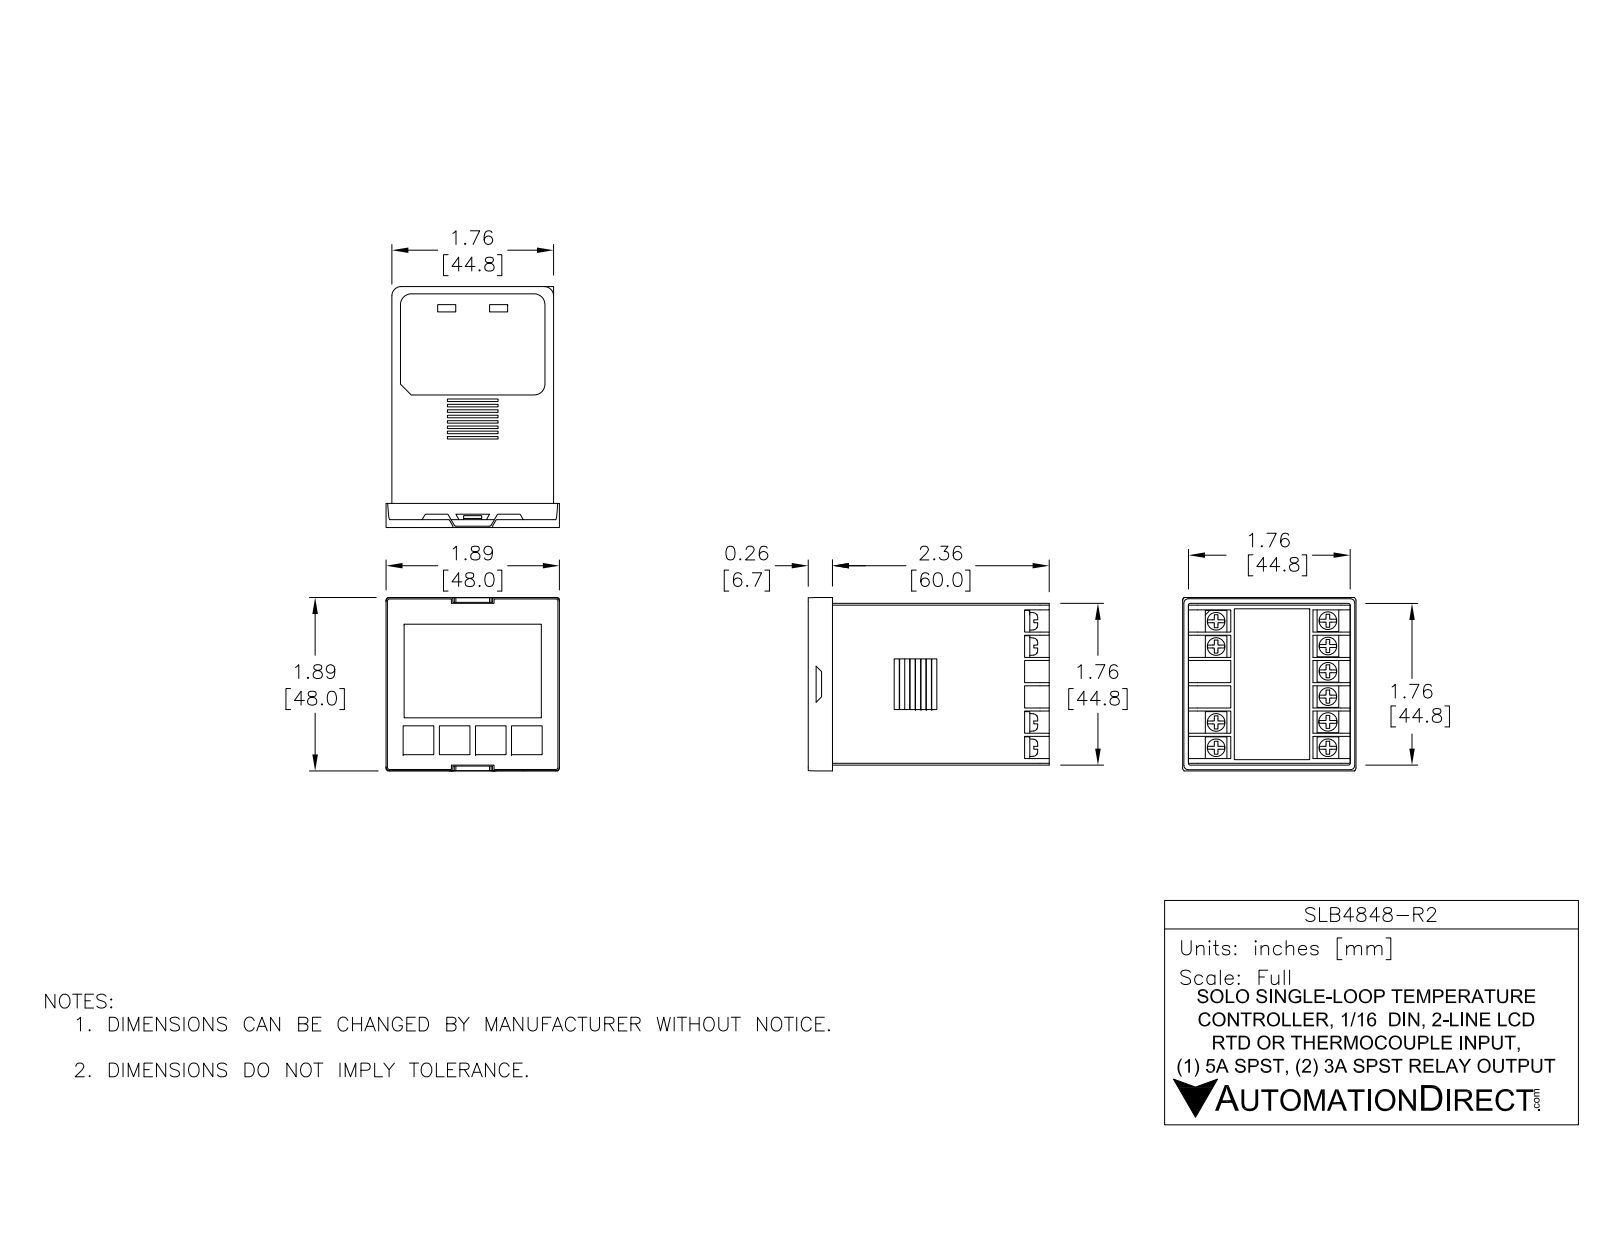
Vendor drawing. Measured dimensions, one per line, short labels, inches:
name: SLB4848-R2
written by: SolidWorks 2017 (AUTOMOTIVE_DESIGN)
unit: in
bodies: 8 solids, 3493 faces (3222 planar, 141 cylindrical, 130 other)
size: 2.628 × 2.234 × 1.89
volume: 7.705 in³; area: 47.25 in²
bosses: 2× ⌀0.21, 2× ⌀0.114
rounds: 36× R0.006, 8× R0.008, 6× R0.02, 6× R0.039, 4× R0.024, 4× R0.04, 4× R0.063, 4× R0.157
face distances: 1.762, 0.049, 1.813, 0.016, 1.746, 0.05, 1.763, 1.764, 1.763, 1.812
